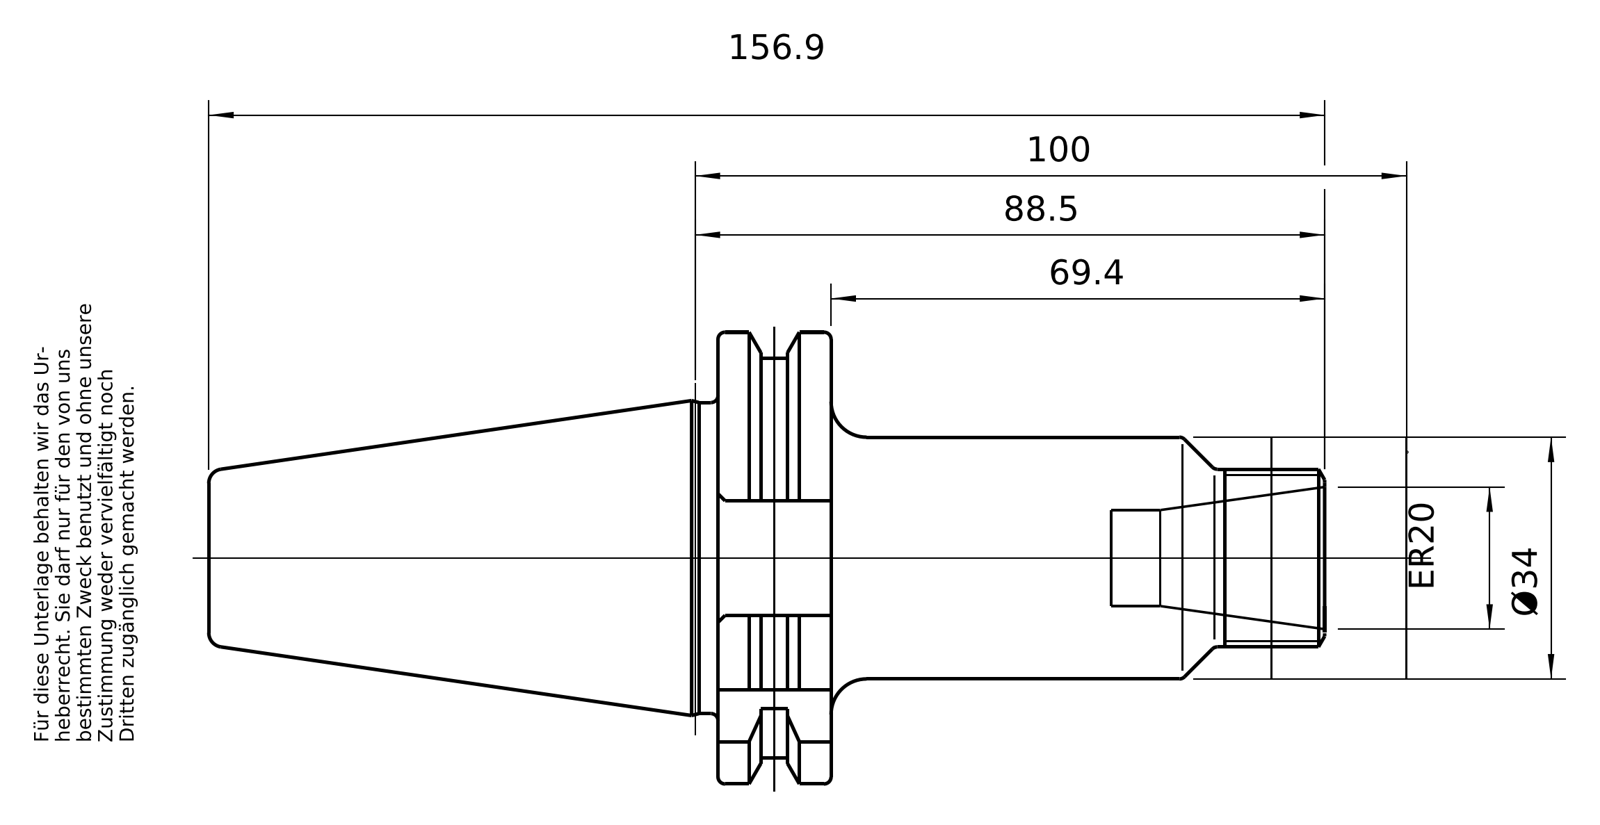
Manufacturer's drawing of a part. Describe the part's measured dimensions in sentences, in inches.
The part is named "40-321-20; 83-912-20; 40-321-20_ASM". Its 3-D file was written by "PRO/ENGINEER BY PARAMETRIC TECHNOLOGY CORPORATION, 2010430 (CONFIG_CONTROL_DESIGN)". It is 2 solids with 125 faces: 29 planar, 28 cylindrical and 68 other. Overall it measures 6.624 by 2.501 by 2.418 inches. Its volume is 10.46 cubic inches and its surface area 48.58 square inches. Round holes: 1 of diameter 0.531, 1 of diameter 0.545, 1 of diameter 0.67, 1 of diameter 0.689. Round bosses or shafts: 1 of diameter 1.722, 1 of diameter 1.339, 1 of diameter 0.984, 1 of diameter 0.63. Partial cylindrical surfaces (rounded edges, fillets, slot ends): 1 of radius 0.053, 1 of radius 1.102, 1 of radius 1.25. The main face-to-face distances are 0.624, 3.063, 2.439, 1.181, 3.811, 3.187, 0.748, 0.272, 0.909, 1.866.
